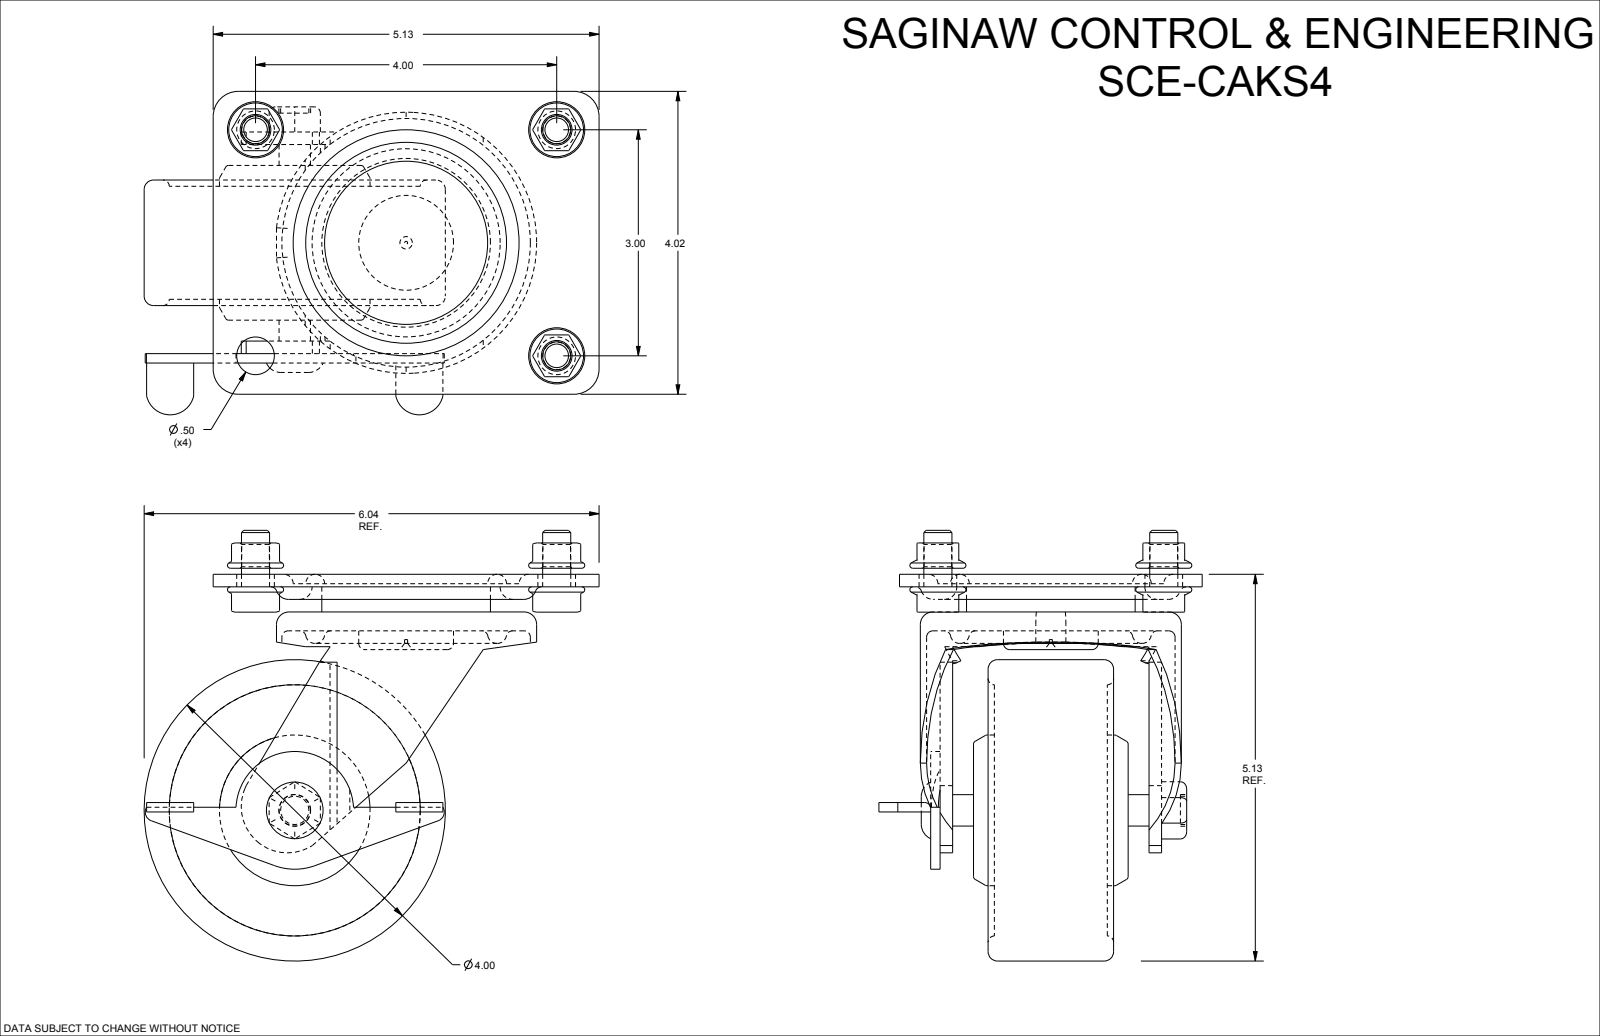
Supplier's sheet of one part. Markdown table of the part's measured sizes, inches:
| quantity | value |
| --- | --- |
| part name | SCE-CAKS4 |
| STEP written by | SolidWorks 2019 (CONFIG_CONTROL_DESIGN) |
| units | inches |
| bodies | 36 solids, 1956 faces (564 planar, 384 cylindrical, 1008 other) |
| overall size | 26.042 × 24.293 × 5.717 |
| volume | 125.9 in³ |
| surface area | 639.5 in² |
| round holes (diameter × count) | 0.367 × 16, 0.5 × 16, 0.04 × 4, 3.3 × 4, 0.421 × 2, 4 × 2 |
| round bosses / shafts (diameter × count) | 0.373 × 16, 3.467 × 4, 2.239 × 4, 1.259 × 4, 2 × 2, 0.417 × 2, 0.375 × 2 |
| partial cylindrical surfaces (radius × count) | 0.01 × 96, 0.083 × 24, 0.333 × 16, 0.32 × 8, 0.122 × 4, 0.08 × 2, 0.167 × 2, 0.614 × 2 |
| main face-to-face distances | 0.167, 20, 0.125, 1.5, 0.277, 0.333, 0.041, 0.5, 2.054, 0.721 |
| hole center spacings | 20, 2.5, 28.284, 3, 4, 5, 18.062, 18.608 |
